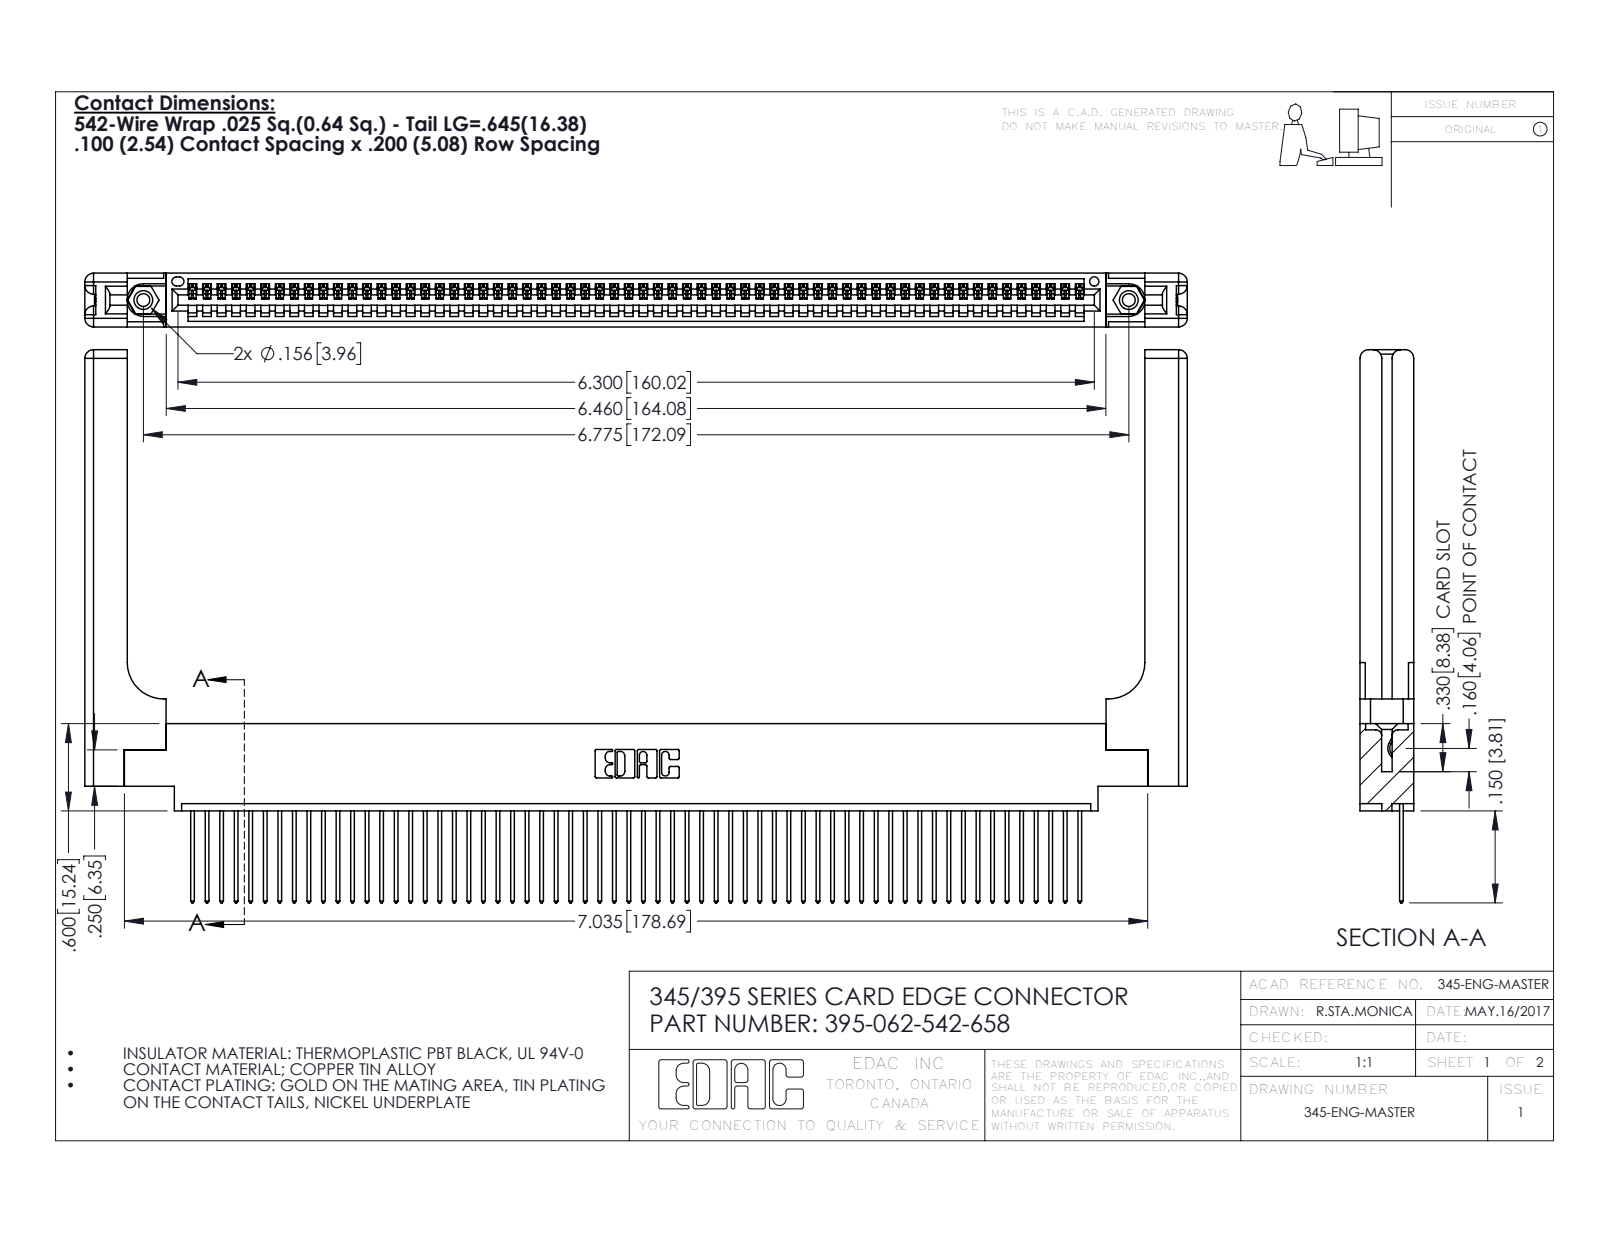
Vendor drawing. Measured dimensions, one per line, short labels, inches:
name: 345-250-001_345-250-001-102; 345-220-058_345-220-058; 345-292-001_345-293-142; 345 Part_0.170 Offset - 0.156 Dia-TH (+1 more)
written by: SolidWorks 2016 (CONFIG_CONTROL_DESIGN)
unit: in
bodies: 67 solids, 3982 faces (2712 planar, 1210 cylindrical, 60 other)
size: 7.579 × 3.802 × 0.37
volume: 1.646 in³; area: 48.24 in²
holes: 2× ⌀0.089, 2× ⌀0.125, 2× ⌀0.156, 1× ⌀0.064
bosses: 2× ⌀0.155
rounds: 124× R0.006, 124× R0.01, 22× R0.01, 16× R0.06, 6× R0.007, 6× R0.031, 3× R0.026, 2× R0.03
face distances: 0.072, 0.298, 0.37, 0.098, 0.272, 0.025, 0.2, 0.225, 0.15, 0.148
hole spacings: 0.27, 6.539, 6.775
